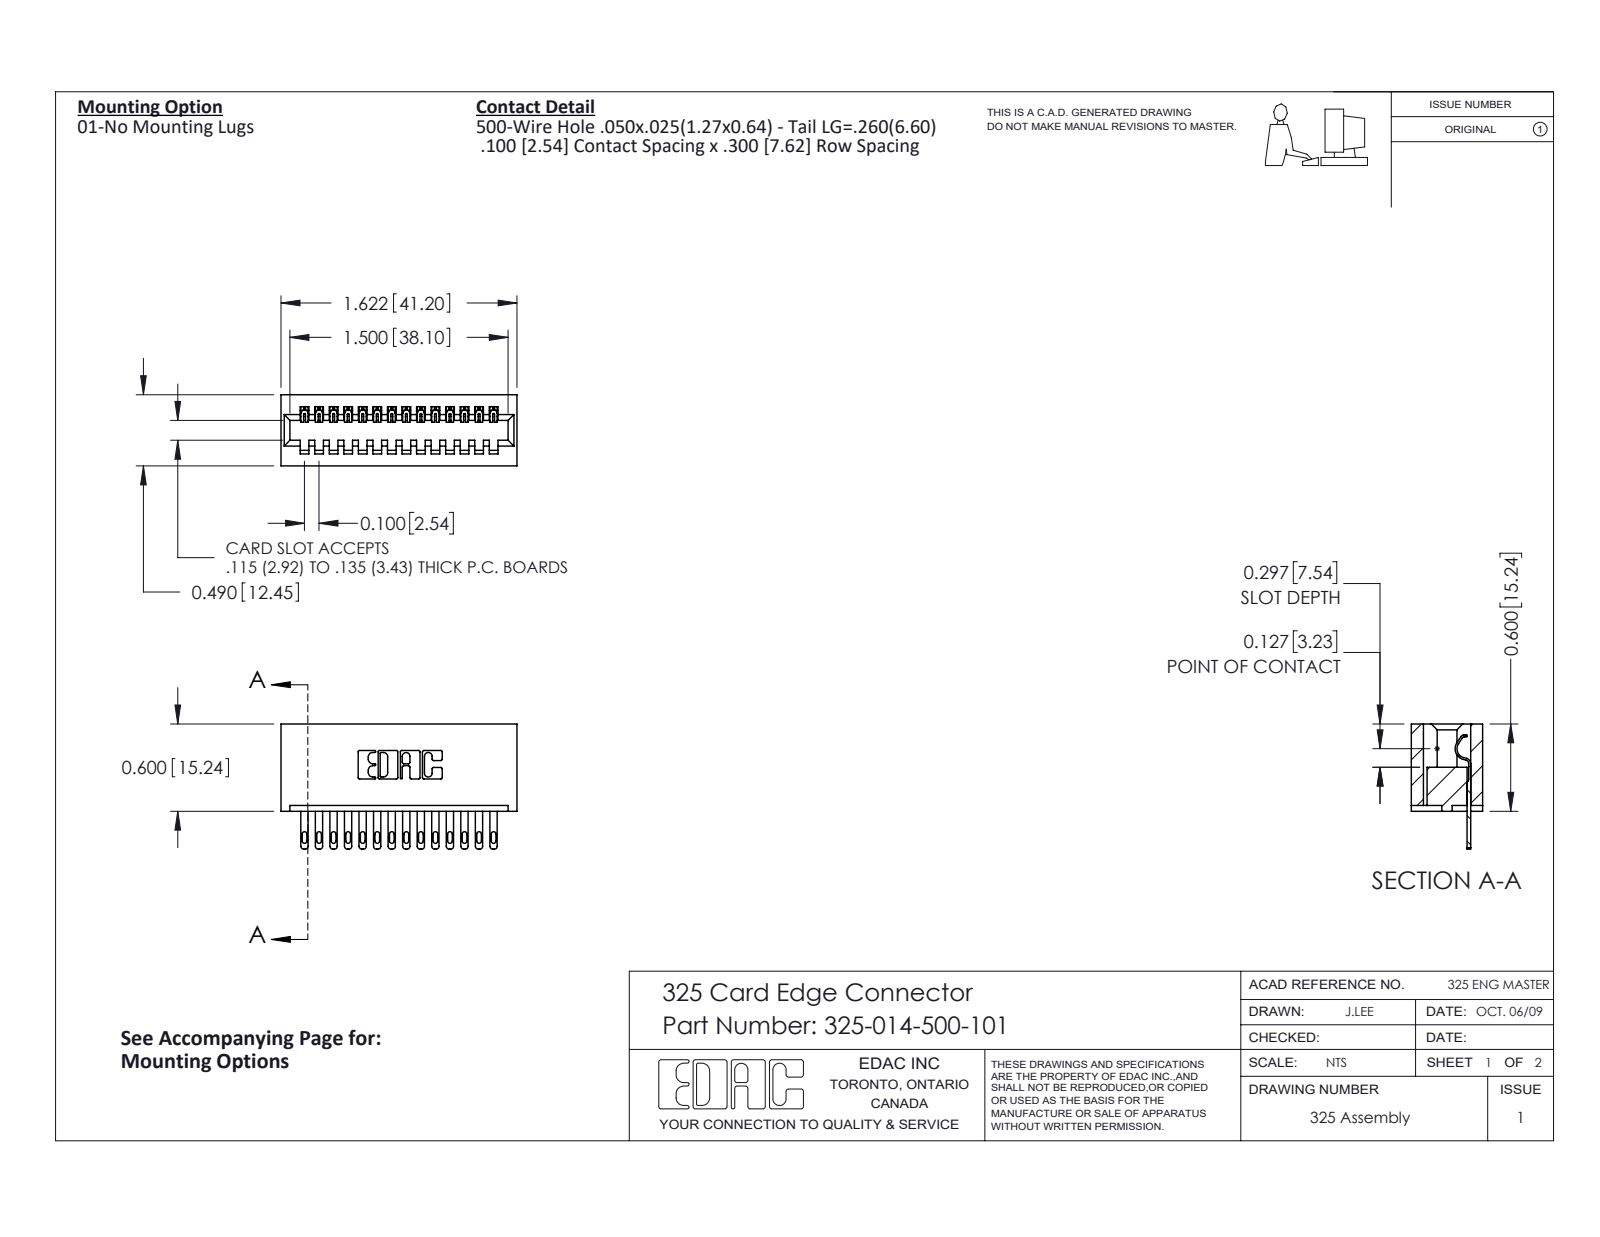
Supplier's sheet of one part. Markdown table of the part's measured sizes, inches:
| quantity | value |
| --- | --- |
| part name | 325 Part_Lugless; 325-292-001_325-293-100; 325-014-500-101 |
| STEP written by | SolidWorks 2016 (CONFIG_CONTROL_DESIGN) |
| units | inches |
| bodies | 15 solids, 862 faces (570 planar, 292 cylindrical, 0 other) |
| overall size | 1.622 × 0.86 × 0.49 |
| volume | 0.341 in³ |
| surface area | 9.541 in² |
| partial cylindrical surfaces (radius × count) | 0.006 × 28, 0.016 × 28, 0.02 × 28, 0.01 × 22, 0.007 × 6, 0.031 × 6, 0.026 × 3, 0.014 × 1 |
| main face-to-face distances | 0.083, 0.407, 0.3, 0.49, 0.1, 0.2, 0.107, 0.383, 0.025, 0.6 |
